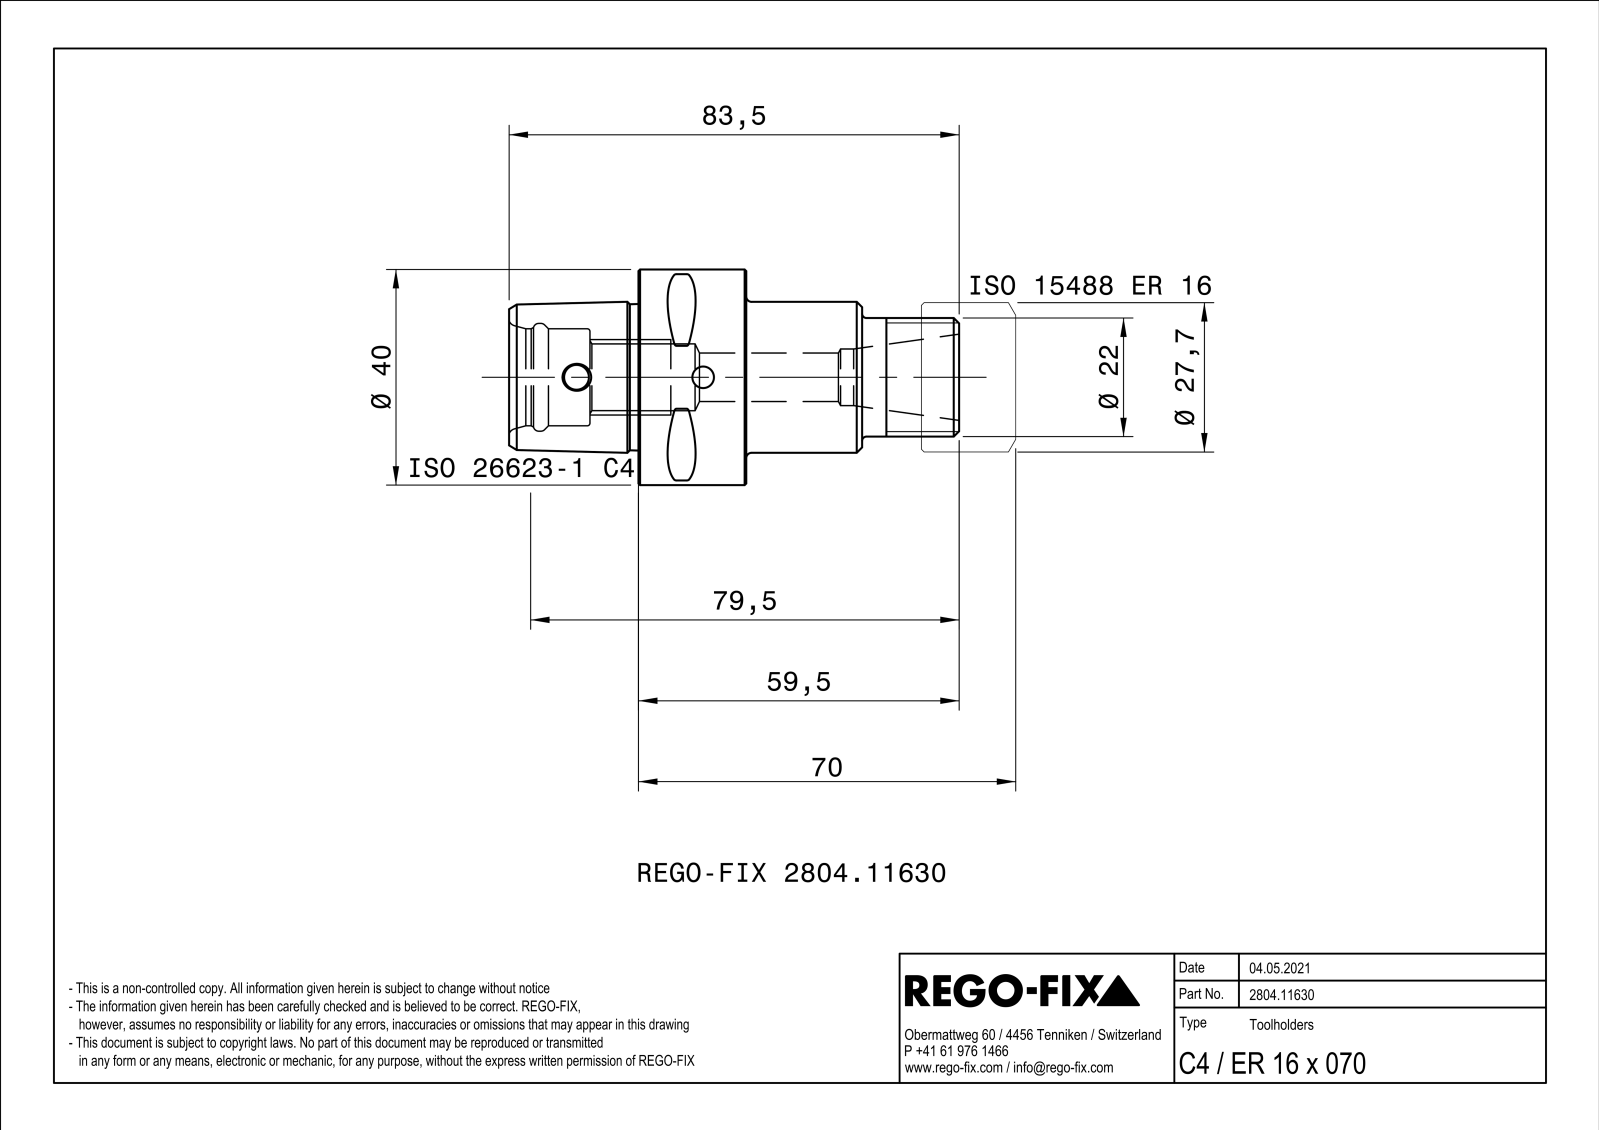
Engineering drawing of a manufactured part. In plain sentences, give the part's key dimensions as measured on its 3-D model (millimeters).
The part is named "NOCUT". Its 3-D file was written by "SIEMENS PLM Software Solid Edge ST10 (AUTOMOTIVE_DESIGN)". It is 1 solid with 109 faces: 21 planar, 23 cylindrical and 65 other. Overall it measures 83.5 by 40 by 40 millimeters. Its volume is 47 368 cubic millimeters and its surface area 13 168 square millimeters. Round holes: 1 of diameter 4, 1 of diameter 4.6, 1 of diameter 9, 1 of diameter 10.5, 1 of diameter 12.38, 1 of diameter 18, 1 of diameter 20. Round bosses or shafts: 1 of diameter 40, 1 of diameter 28, 1 of diameter 22. Partial cylindrical surfaces (rounded edges, fillets, slot ends): 8 of radius 0.5, 1 of radius 3. The main face-to-face distances are 20, 44, 24, 15.52, 39.5, 59.5, 83.5, 18, 21.5, 41.5. The hole center spacings are 23.5.
